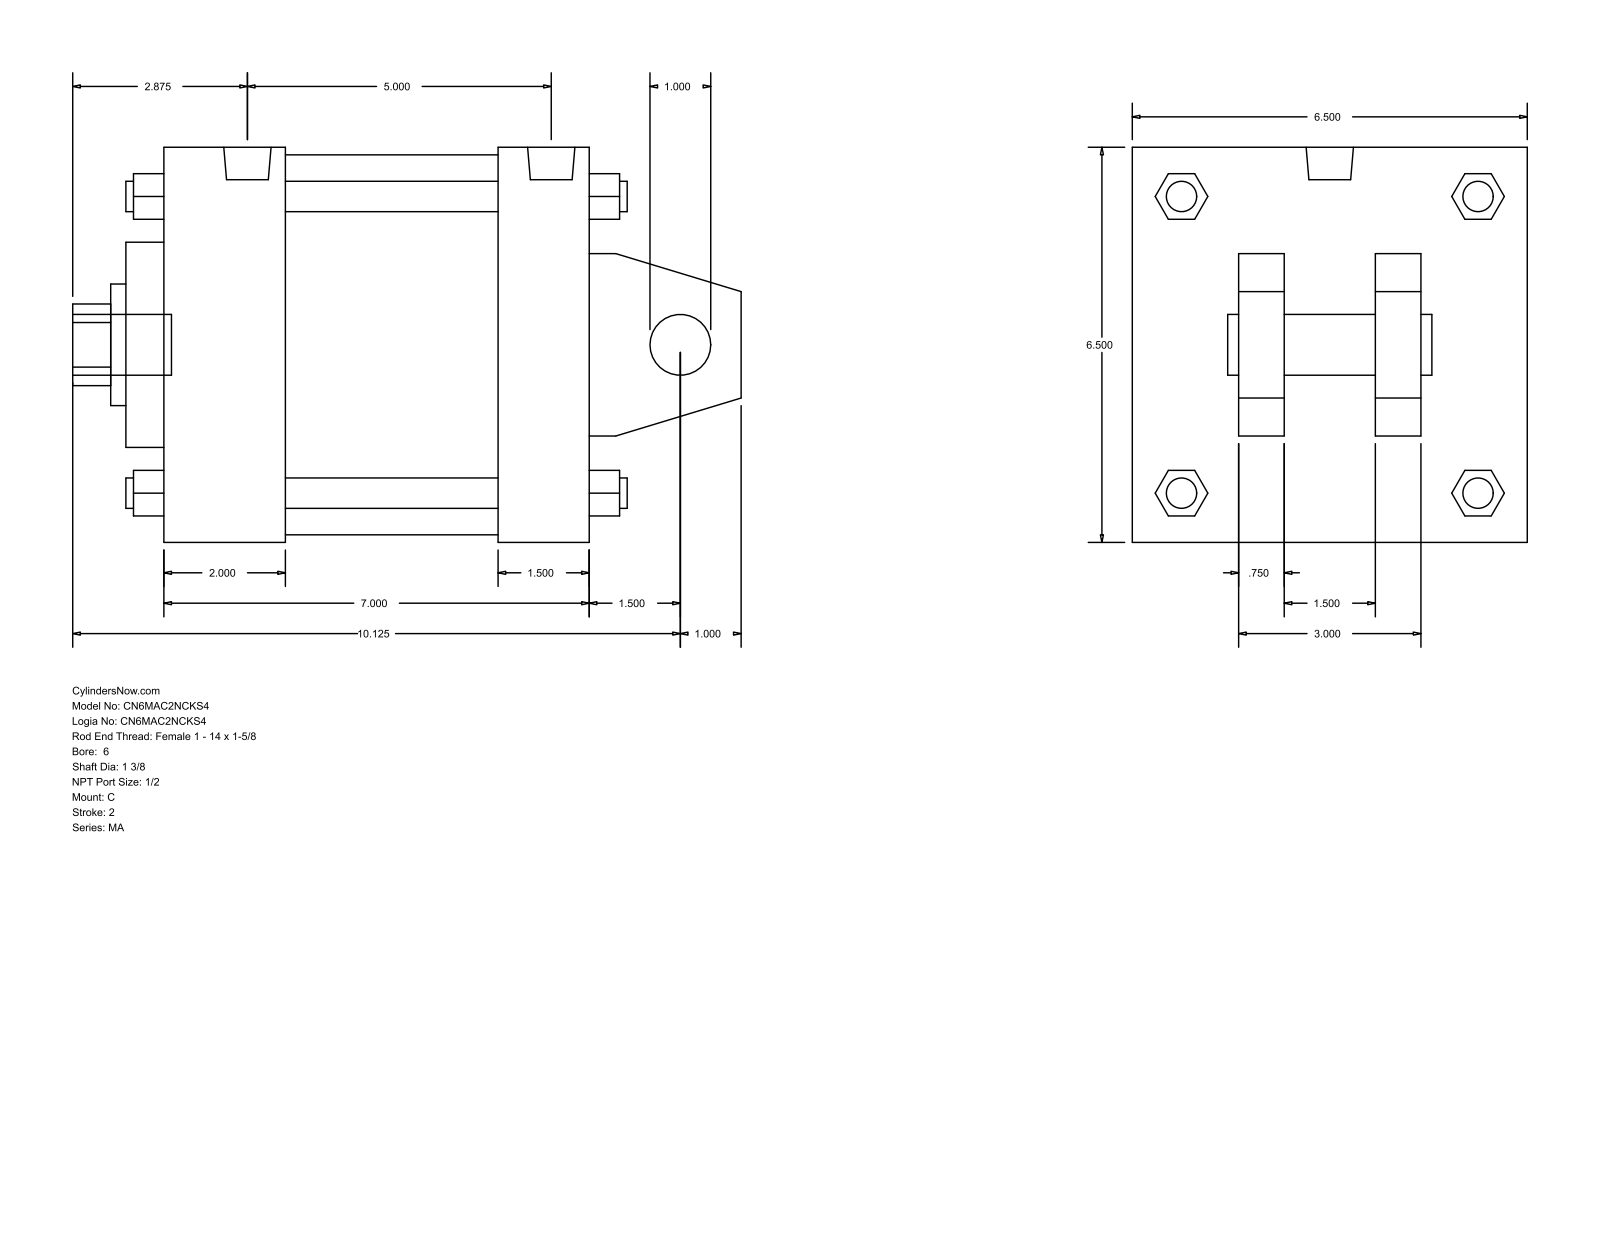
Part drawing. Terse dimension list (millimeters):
name: MA_C__0600_1.375
written by: GSSL Pune (CONFIG_CONTROL_DESIGN)
unit: mm
bodies: 0 solids, 141 faces (109 planar, 32 cylindrical, 0 other)
size: 279.4 × 165.1 × 165.1
holes: 1× ⌀25.4, 1× ⌀34.92, 1× ⌀50.8, 1× ⌀85.72, 1× ⌀158.75
bosses: 4× ⌀17.46, 4× ⌀12.7, 2× ⌀19.77, 1× ⌀25.4
rounds: 1× R17.06
face distances: 165.1, 177.8, 38.1, 19.05, 63.5, 101.6, 50.8, 44.45, 120.65, 139.7
